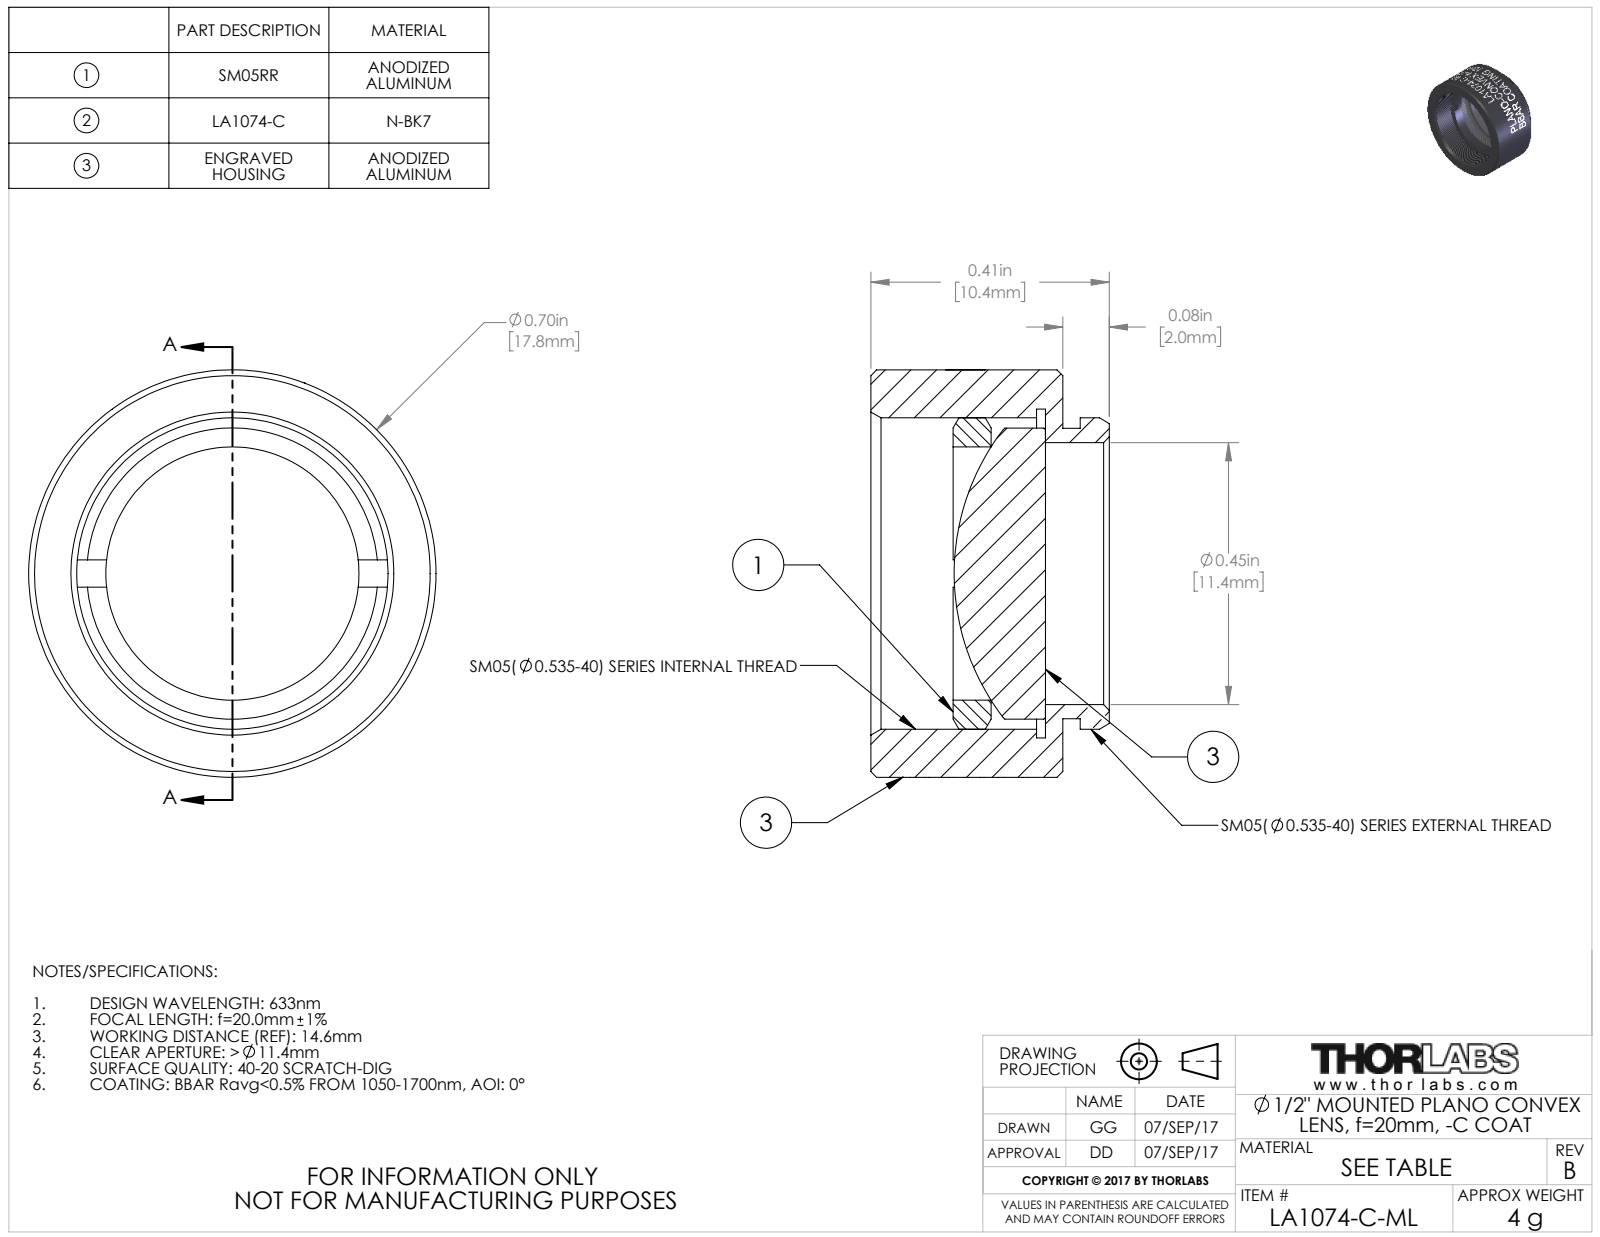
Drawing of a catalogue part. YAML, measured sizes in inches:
part_name: "24393-E0W"
step_written_by: "SolidWorks 2016 (CONFIG_CONTROL_DESIGN)"
units: inches
bodies: {solids: 3, faces: 282, planar: 94, cylindrical: 109, other: 79}
overall_size: [0.7, 0.7, 0.41]
volume: 0.085
surface_area: 2.872
round_holes:
  - {diameter: 0.435, count: 1}
  - {diameter: 0.45, count: 1}
  - {diameter: 0.535, count: 1}
  - {diameter: 0.565, count: 1}
round_bosses_or_shafts:
  - {diameter: 0.7, count: 1}
  - {diameter: 0.535, count: 1}
  - {diameter: 0.5, count: 1}
  - {diameter: 0.499, count: 1}
partial_cylinders:
  - {radius: 0.35, count: 1}
face_to_face_distances: [0.03, 0.3, 0.33, 0.124, 0.093, 0.207, 0.158, 0.189, 0.065, 0.142]
